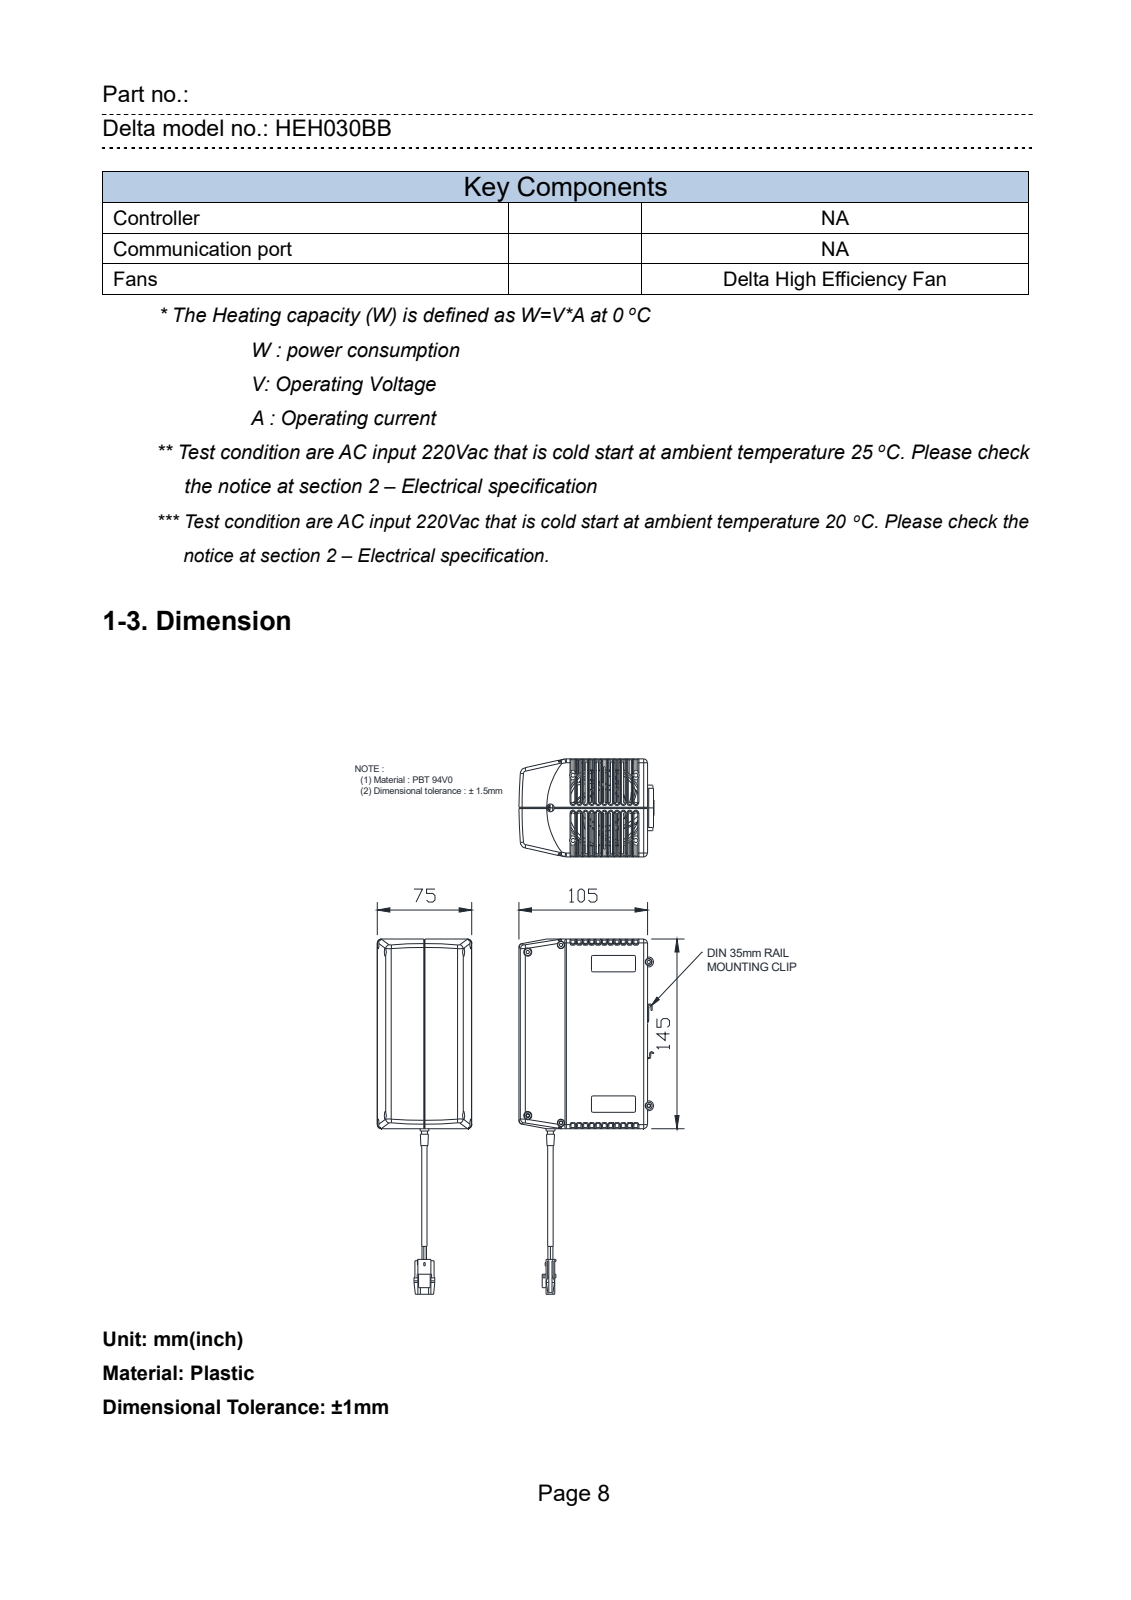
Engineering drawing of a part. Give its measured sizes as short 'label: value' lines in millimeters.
name: HEH030BB
written by: SolidWorks 2016 (AUTOMOTIVE_DESIGN)
unit: mm
bodies: 0 solids, 1308 faces (489 planar, 469 cylindrical, 350 other)
size: 271.6 × 108.41 × 75
holes: 4× ⌀4.5, 1× ⌀4.09, 1× ⌀6, 1× ⌀33, 1× ⌀57.2
bosses: 3× ⌀1.9, 1× ⌀7, 1× ⌀4.8, 1× ⌀4.19
rounds: 56× R0.8, 46× R1, 33× R1.5, 18× R0.5, 13× R3, 5× R2.5, 4× R0.3, 4× R1.6
face distances: 20, 1.8, 8.8, 28.8, 6.1, 10.6, 21.8, 7, 18.2, 11.2
hole spacings: 35.36, 50, 70.71, 30.76, 31.09, 43.2, 72.57, 72.71
